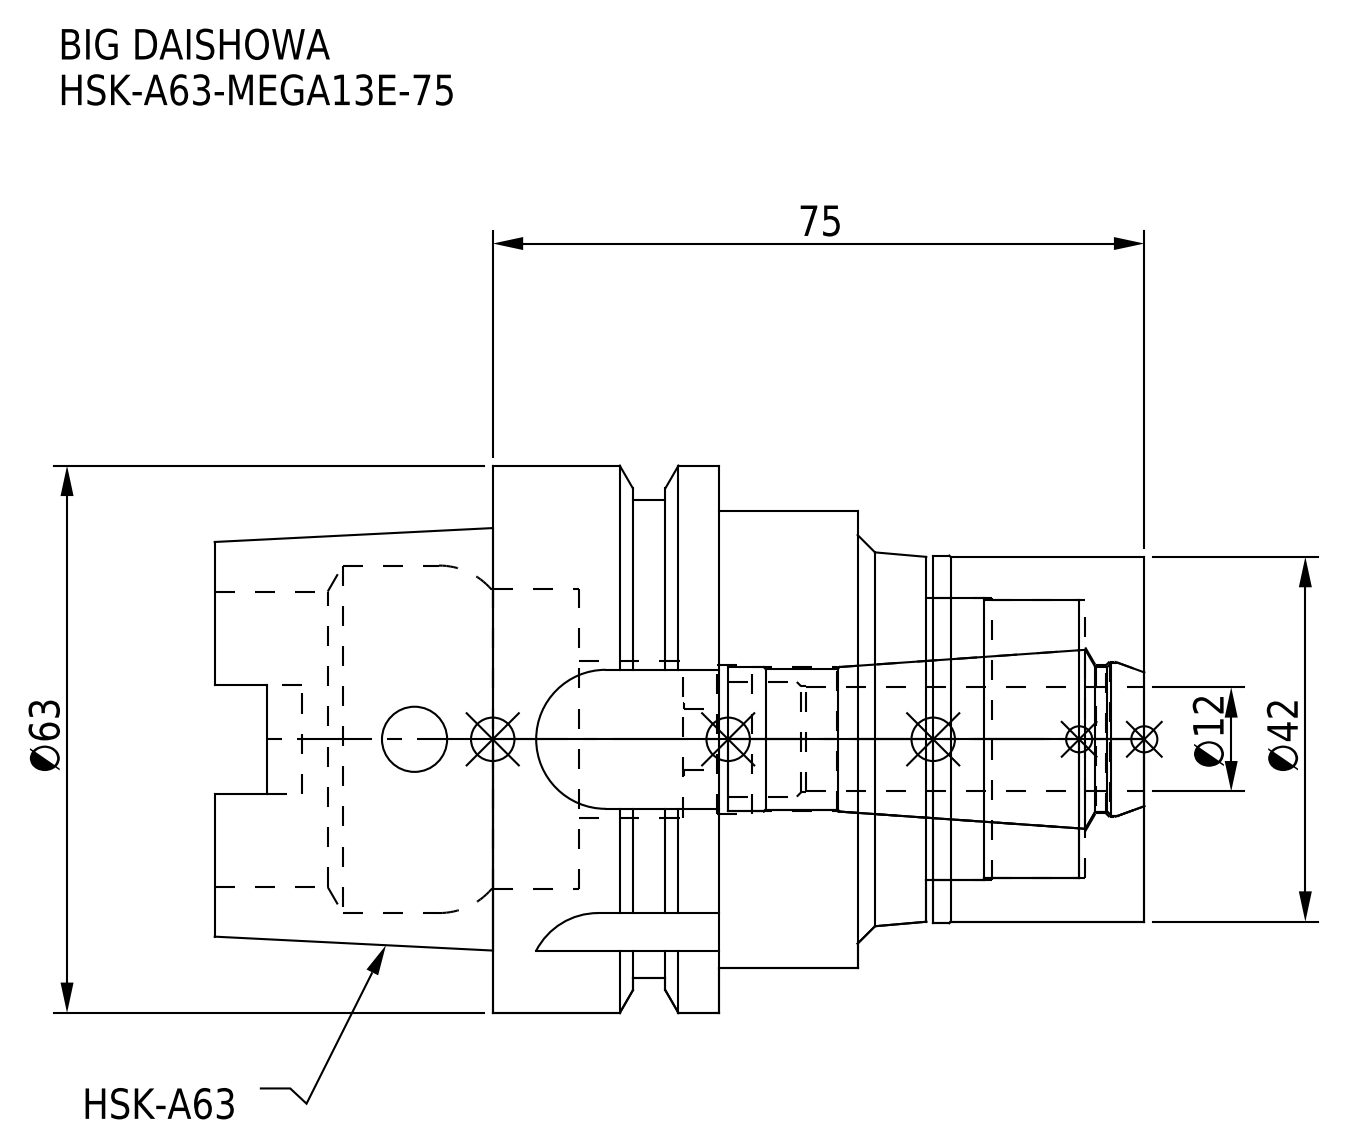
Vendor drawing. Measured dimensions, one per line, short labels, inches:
name: HSK-A63-MEGA13E-75-120.stp; DXF_TEMP_ASSY_ASM_4_ASM.stp; HSK-A63-MEGA13E-75_1.stp; MEN13_1.stp (+3 more)
written by: SolidWorks 2019 (CONFIG_CONTROL_DESIGN)
unit: in
bodies: 2 solids, 127 faces (45 planar, 54 cylindrical, 28 other)
size: 4.213 × 2.48 × 2.48
volume: 9.134 in³; area: 58.24 in²
holes: 1× ⌀0.276, 1× ⌀0.295, 1× ⌀0.331, 1× ⌀0.654, 1× ⌀0.669, 1× ⌀0.677, 1× ⌀0.705, 1× ⌀0.709, 1× ⌀1.26, 1× ⌀1.28, 1× ⌀1.339, 1× ⌀1.358
bosses: 1× ⌀2.48, 1× ⌀2.165, 1× ⌀2.071, 1× ⌀1.665, 1× ⌀1.654
rounds: 2× R0.11, 2× R0.113, 2× R0.315, 1× R0.354
face distances: 2.953, 1.024, 1.929, 2.561, 0.632, 0.392, 0.957, 0.972, 1.604, 1.996
